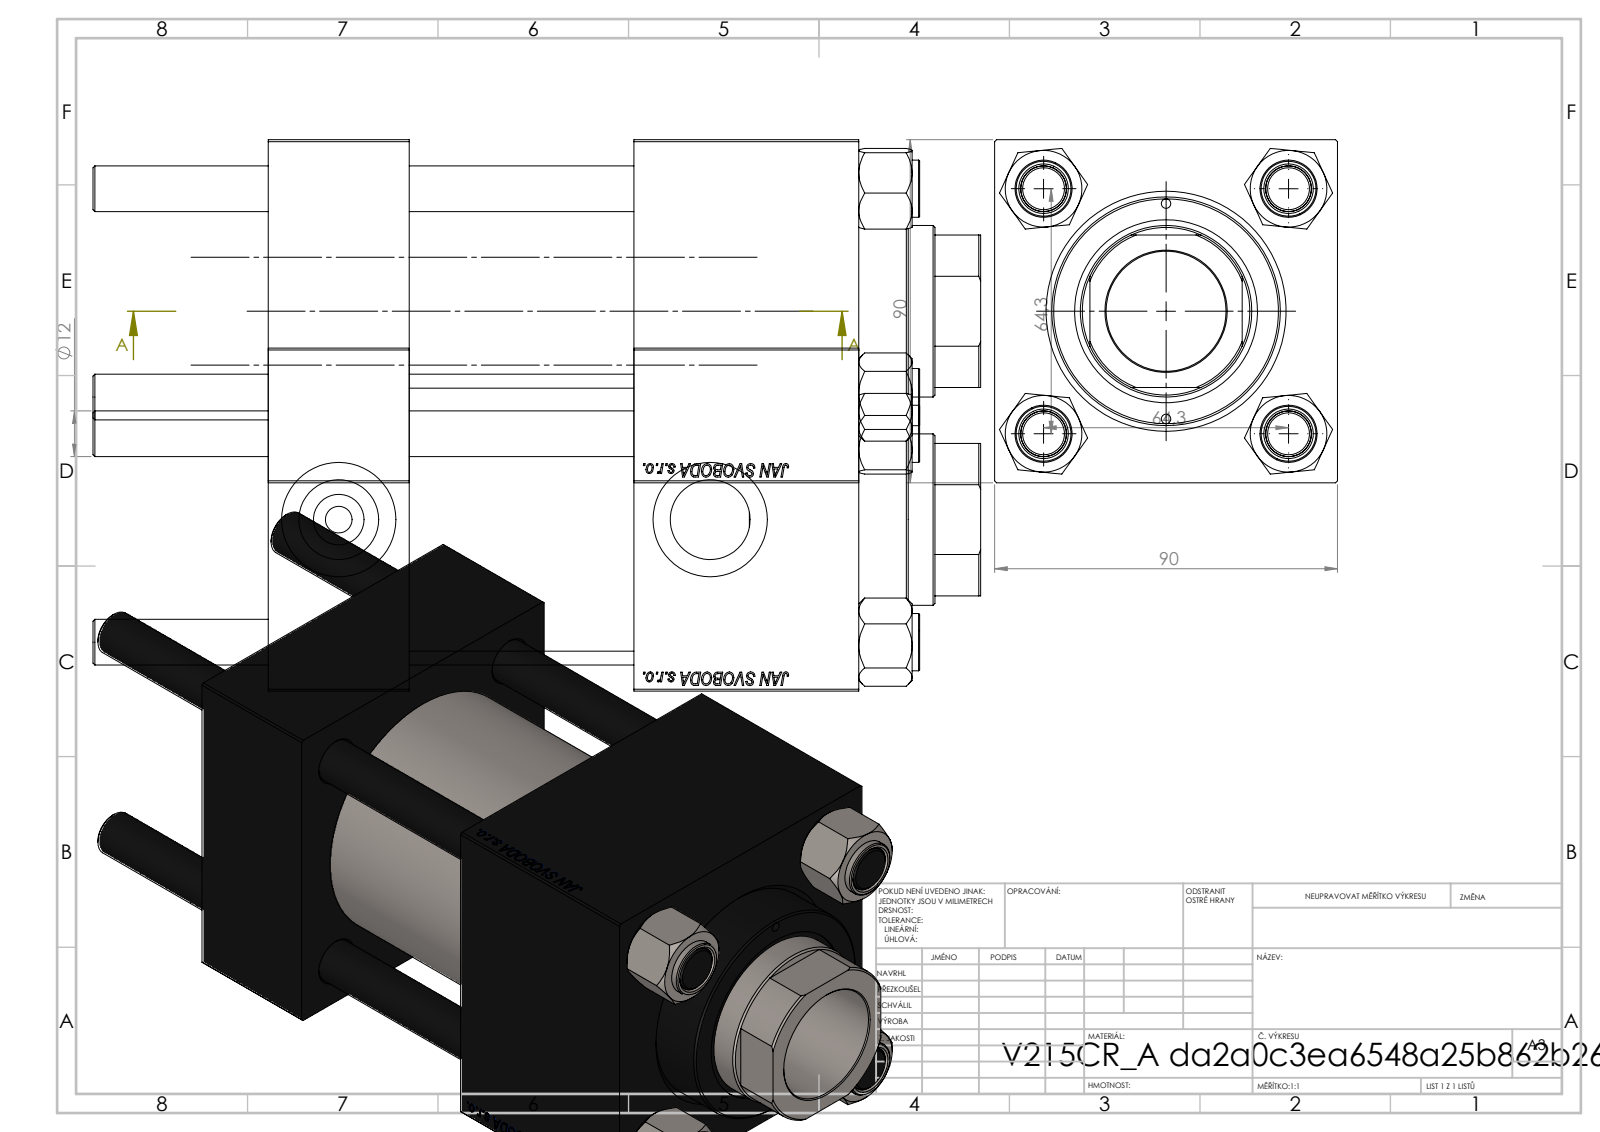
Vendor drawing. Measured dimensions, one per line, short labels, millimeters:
name: V215_VC_A; V215CR_VCP; CR025_012_A_0_G_A_G_M_020_+#_##_TYCINKA; NUT_M5 (+1 more)
written by: SolidWorks 2019 (CONFIG_CONTROL_DESIGN)
unit: mm
bodies: 11 solids, 1137 faces (521 planar, 80 cylindrical, 536 other)
size: 233 × 90 × 90
volume: 1 032 000 mm³; area: 206 348 mm²
holes: 4× ⌀12, 2× ⌀2.5, 2× ⌀7, 2× ⌀20.96, 2× ⌀30, 1× ⌀31.5, 1× ⌀45, 1× ⌀48, 1× ⌀50, 1× ⌀60, 1× ⌀63
bosses: 4× ⌀15, 1× ⌀69
rounds: 1× R22
face distances: 90, 59, 37, 155, 118, 96, 126.3, 89.3, 30.3, 28.7
hole spacings: 32.39, 45.47, 64.3, 68.42, 28.25, 90.93, 56.5, 97.5
